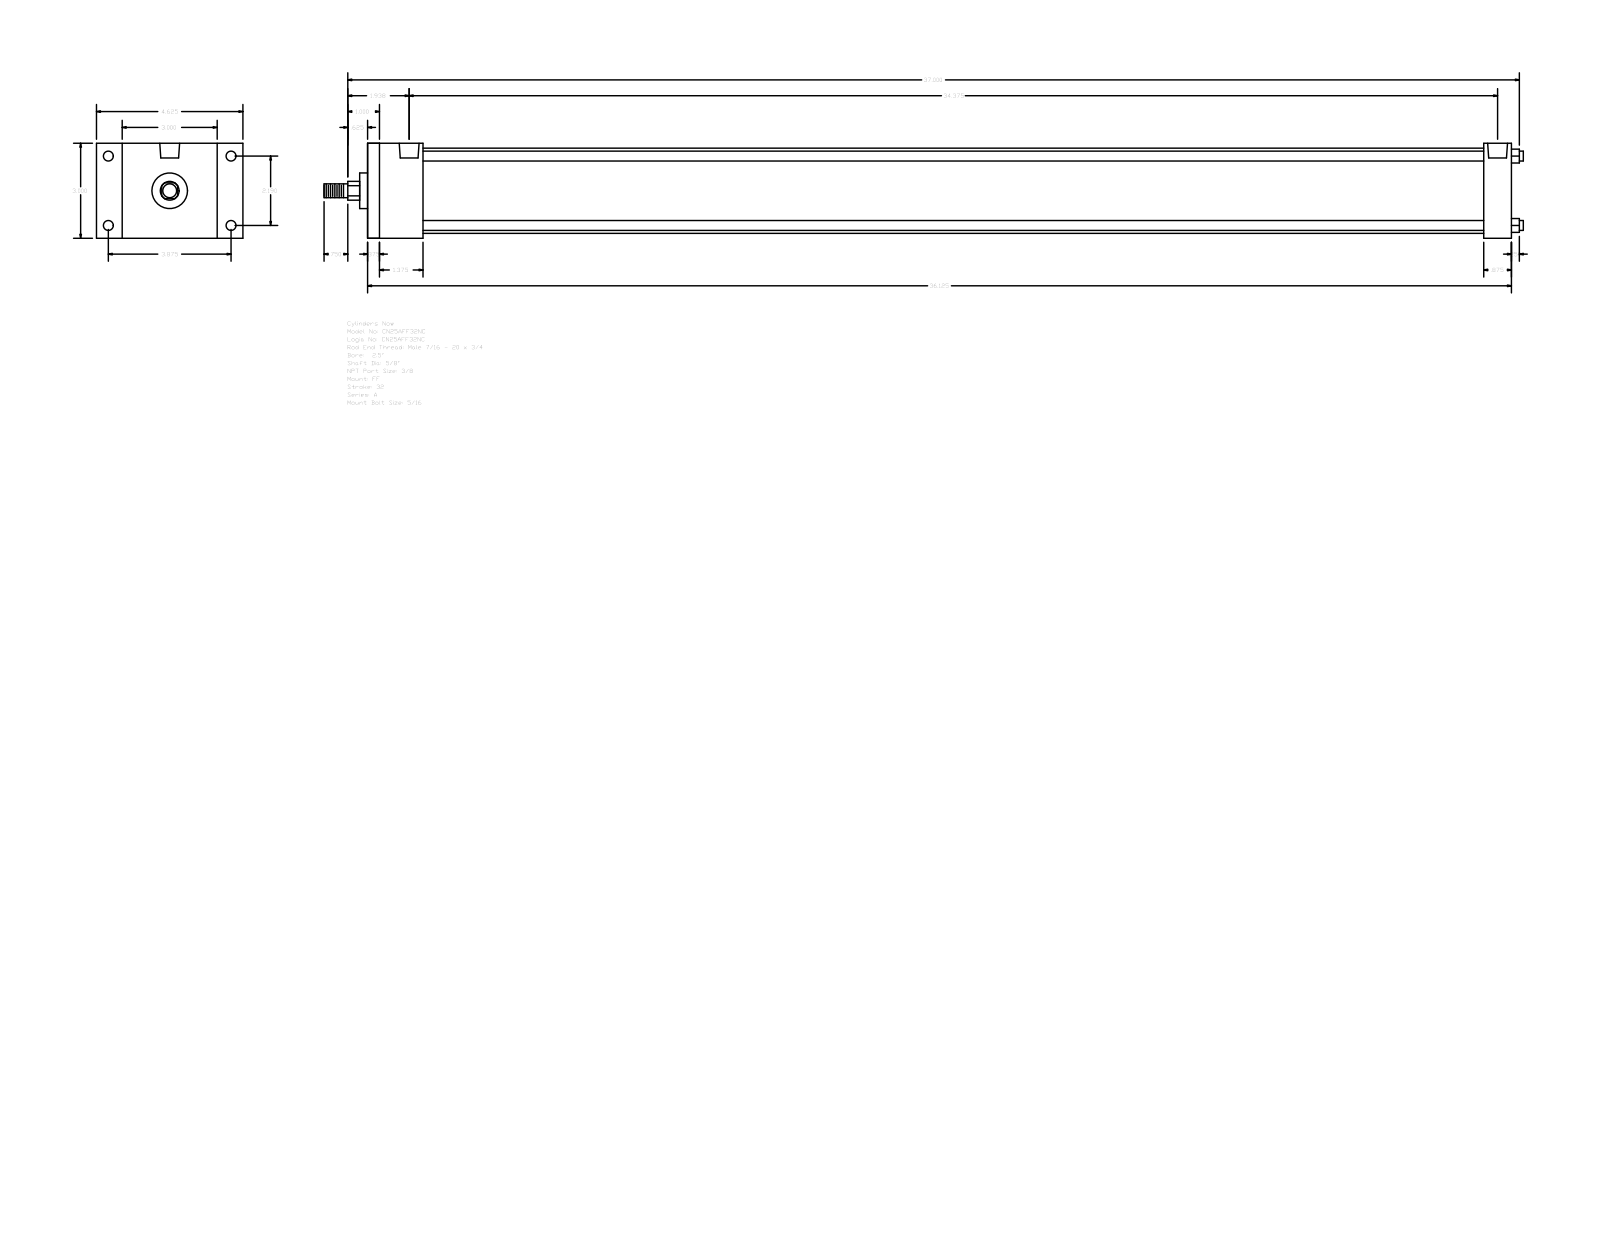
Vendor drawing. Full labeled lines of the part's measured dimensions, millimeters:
Part name (STEP PRODUCT): A_FF__0250_0.625
STEP written by: GSSL Pune (CONFIG_CONTROL_DESIGN)
Units: millimetres
Bodies: 0 solids, 92 faces (64 planar, 28 cylindrical, 0 other)
Overall size (bounding box): 962.02 × 117.47 × 76.2
Round holes (diameter × count): ⌀5.56 ×4, ⌀7.94 ×4, ⌀15.93 ×2
Round bosses / shafts (diameter × count): ⌀7.94 ×4, ⌀68.33 ×1, ⌀28.57 ×1, ⌀15.88 ×1, ⌀11.11 ×1
Partial cylindrical surfaces — rounded edges, fillets, slot ends (radius × count): R7.54 ×1
Main face-to-face distances: 76.2, 917.57, 9.52, 908.05, 44.45, 34.93, 895.35, 885.83, 850.9, 873.12
Hole centre spacings: 2.38, 55.62, 98.42, 113.05, 875.51, 877.89, 873.13
